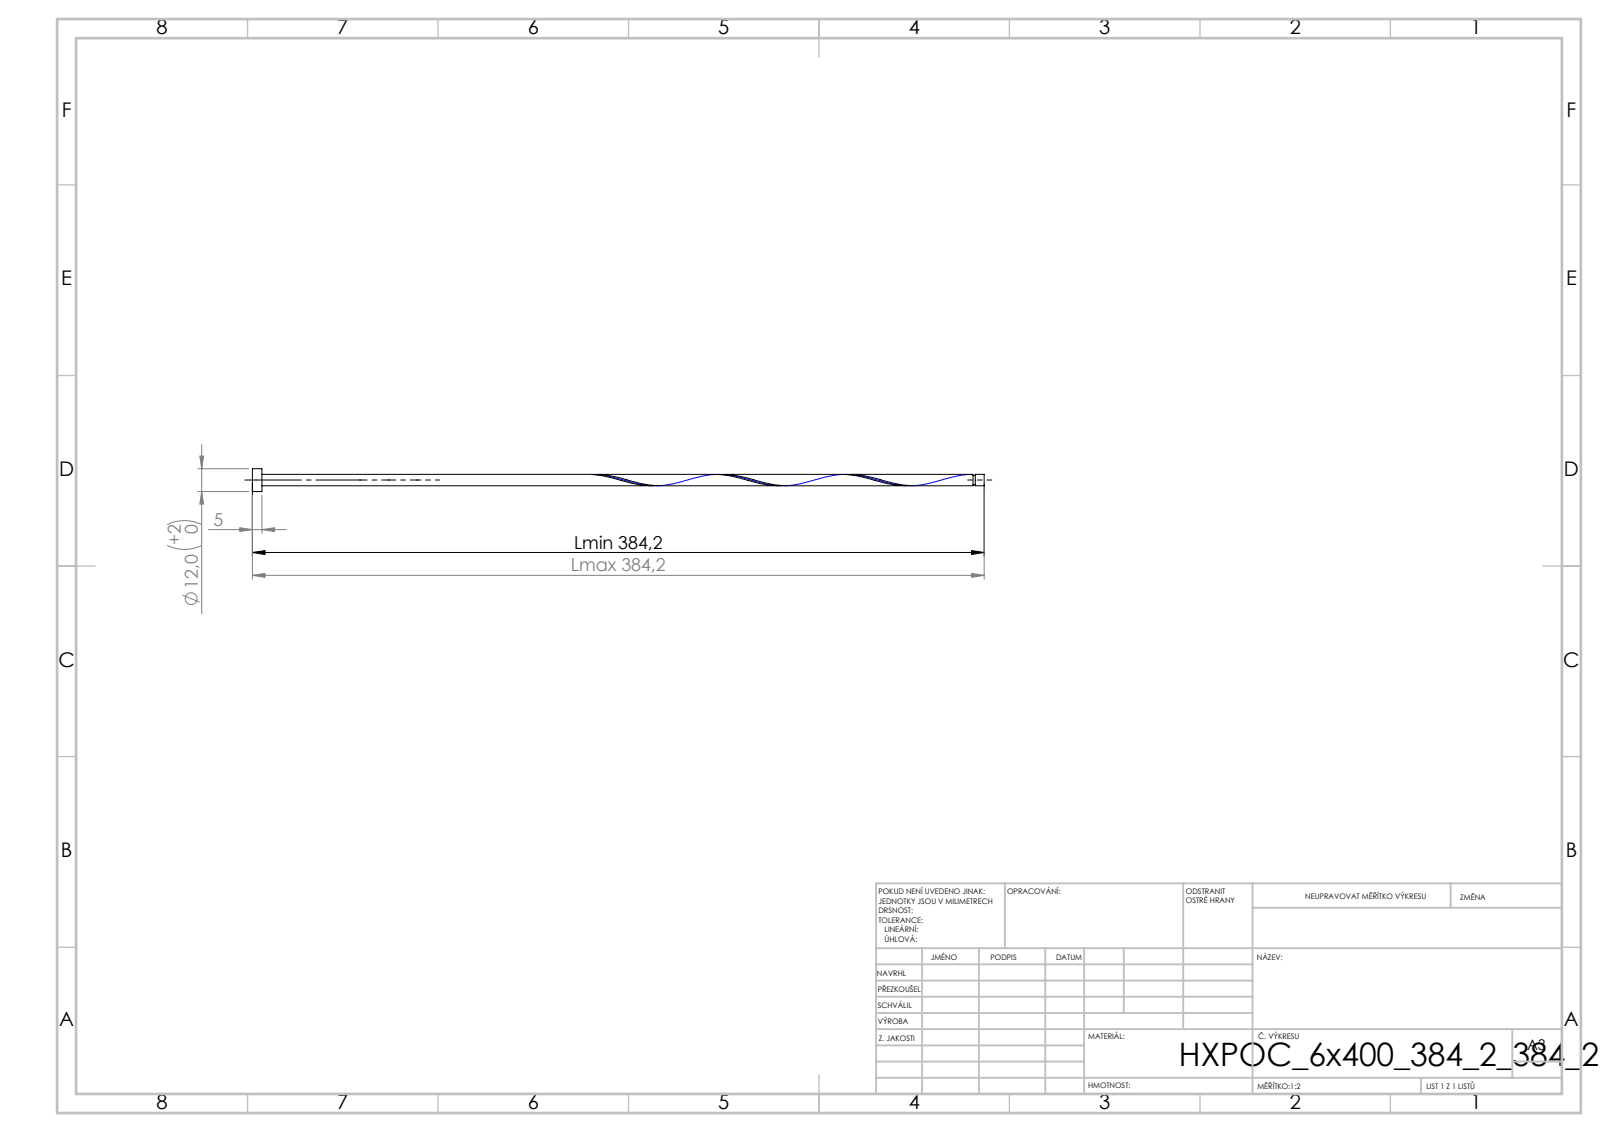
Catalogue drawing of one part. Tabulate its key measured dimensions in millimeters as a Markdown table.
| quantity | value |
| --- | --- |
| STEP written by | SolidWorks 2019 (CONFIG_CONTROL_DESIGN) |
| units | millimeters |
| bodies | 1 solid, 16 faces (6 planar, 9 cylindrical, 1 other) |
| overall size | 384.2 × 12 × 12 |
| volume | 13 681 mm³ |
| surface area | 10 212 mm² |
| round bosses / shafts (diameter × count) | 12 × 1, 6 × 1, 4.8 × 1 |
| main face-to-face distances | 5, 384.2, 379.2, 379.48, 374.48, 4.72, 378.28, 373.28, 1.2, 5.92 |
